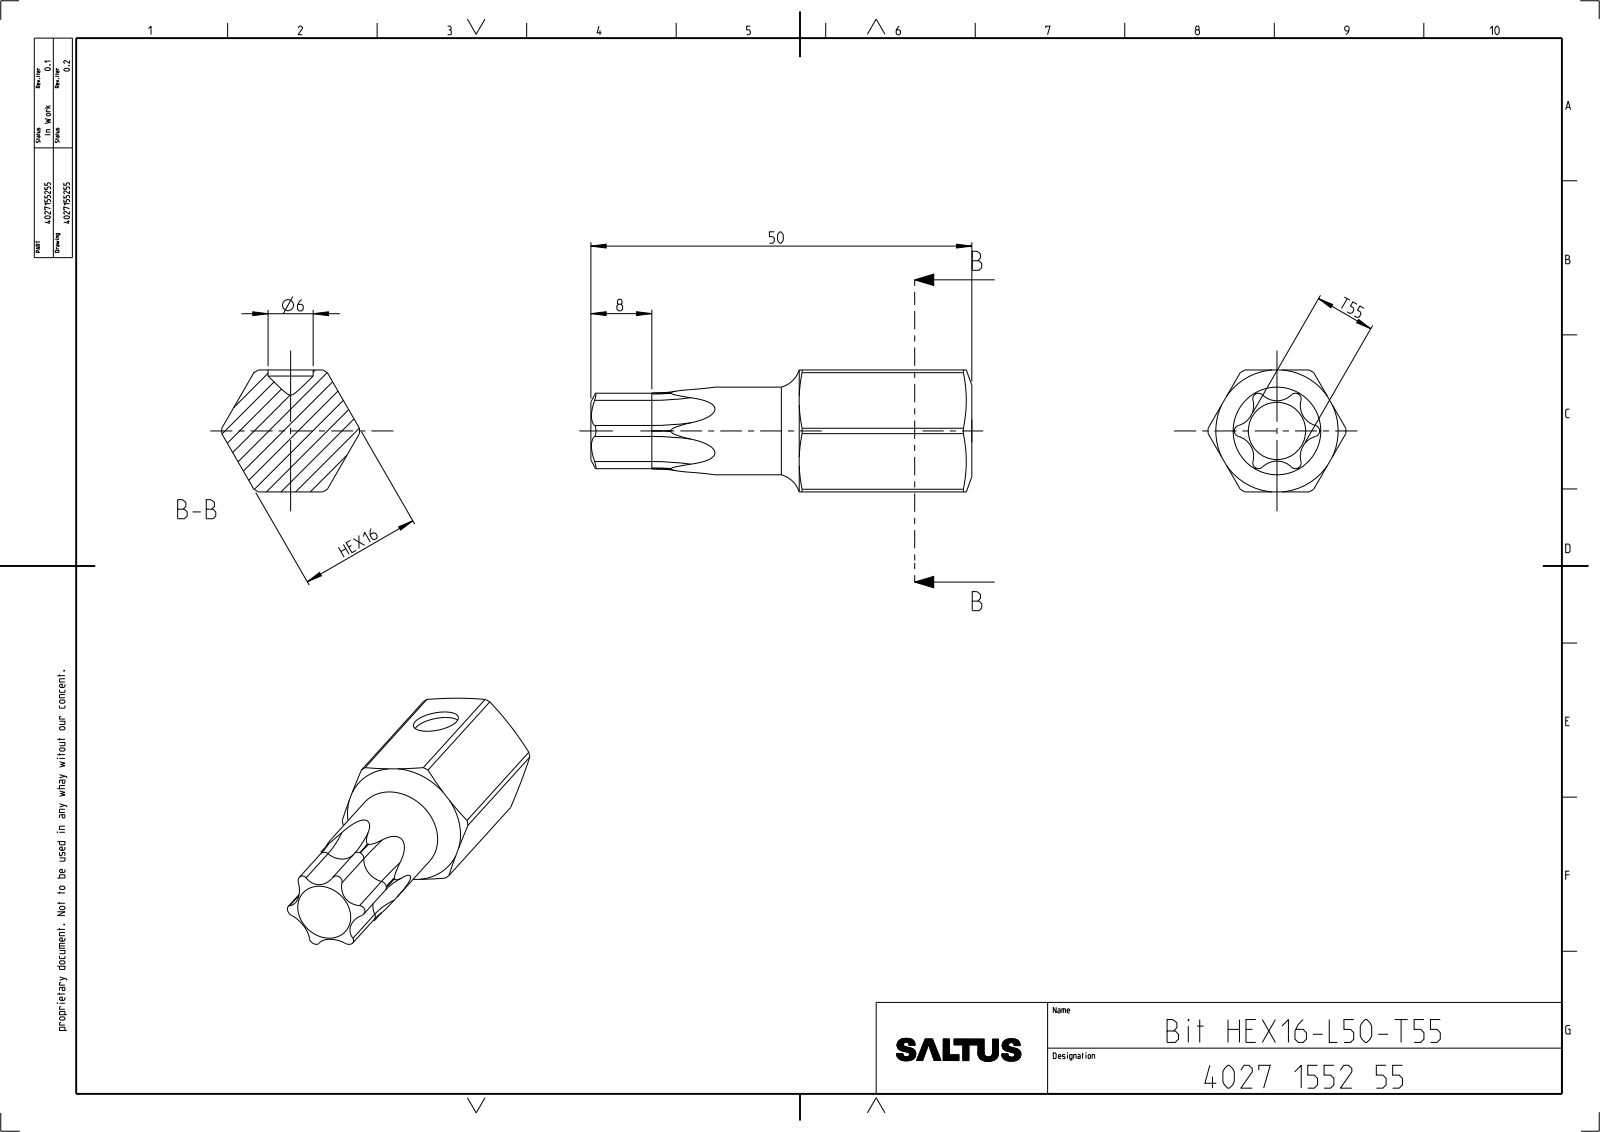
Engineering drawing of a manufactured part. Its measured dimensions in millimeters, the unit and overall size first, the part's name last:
Units: millimetres
Overall size (bounding box): 50 × 18.08 × 16
Round holes (diameter × count): ⌀6 ×1
Round bosses / shafts (diameter × count): ⌀11.5 ×1
Partial cylindrical surfaces — rounded edges, fillets, slot ends (radius × count): R0.75 ×6, R2.71 ×6, R9.04 ×1
Main face-to-face distances: 16, 50
Volume: 7 342 mm³ · Surface area: 2 589 mm²
Bodies: 1 solid, 74 faces (8 planar, 22 cylindrical, 44 other)
Part name (STEP PRODUCT): 4027155255
STEP written by: CREO PARAMETRIC BY PTC INC, 2022414 (CONFIG_CONTROL_DESIGN)
